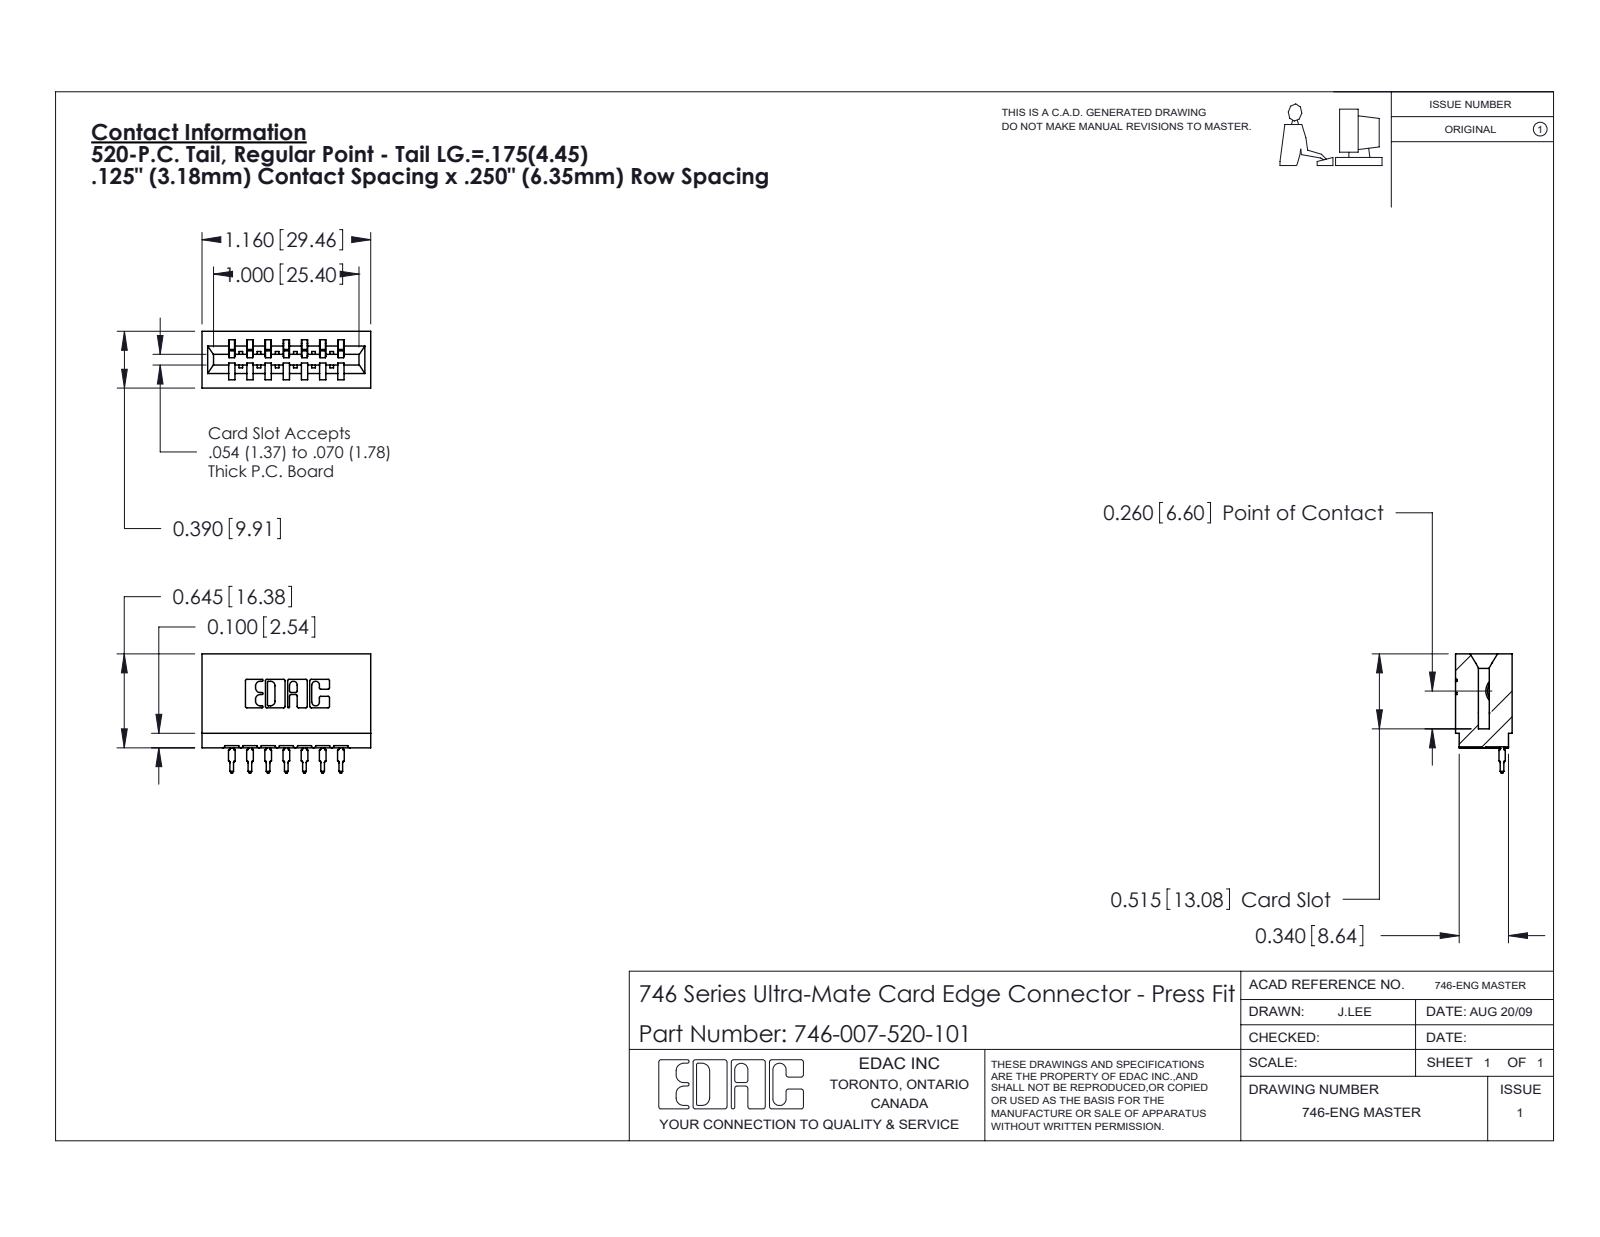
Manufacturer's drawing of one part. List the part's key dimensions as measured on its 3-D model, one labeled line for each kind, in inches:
Part name (STEP PRODUCT): 746 Part_.515 Slot Depth - 01; 746-007-520-101; 746-292-001_520
STEP written by: SolidWorks 2020 (CONFIG_CONTROL_DESIGN)
Units: inches
Bodies: 8 solids, 853 faces (496 planar, 175 cylindrical, 182 other)
Overall size (bounding box): 1.16 × 0.819 × 0.39
Volume: 0.202 in³ · Surface area: 6.608 in²
Partial cylindrical surfaces — rounded edges, fillets, slot ends (radius × count): R0.01 ×22, R0.021 ×14, R0.015 ×8, R0.007 ×6, R0.031 ×6, R0.005 ×4, R0.011 ×4, R0.026 ×3
Main face-to-face distances: 0.25, 0.042, 0.333, 0.125, 0.5, 0.125, 0.057, 0.292, 0.208, 0.39
